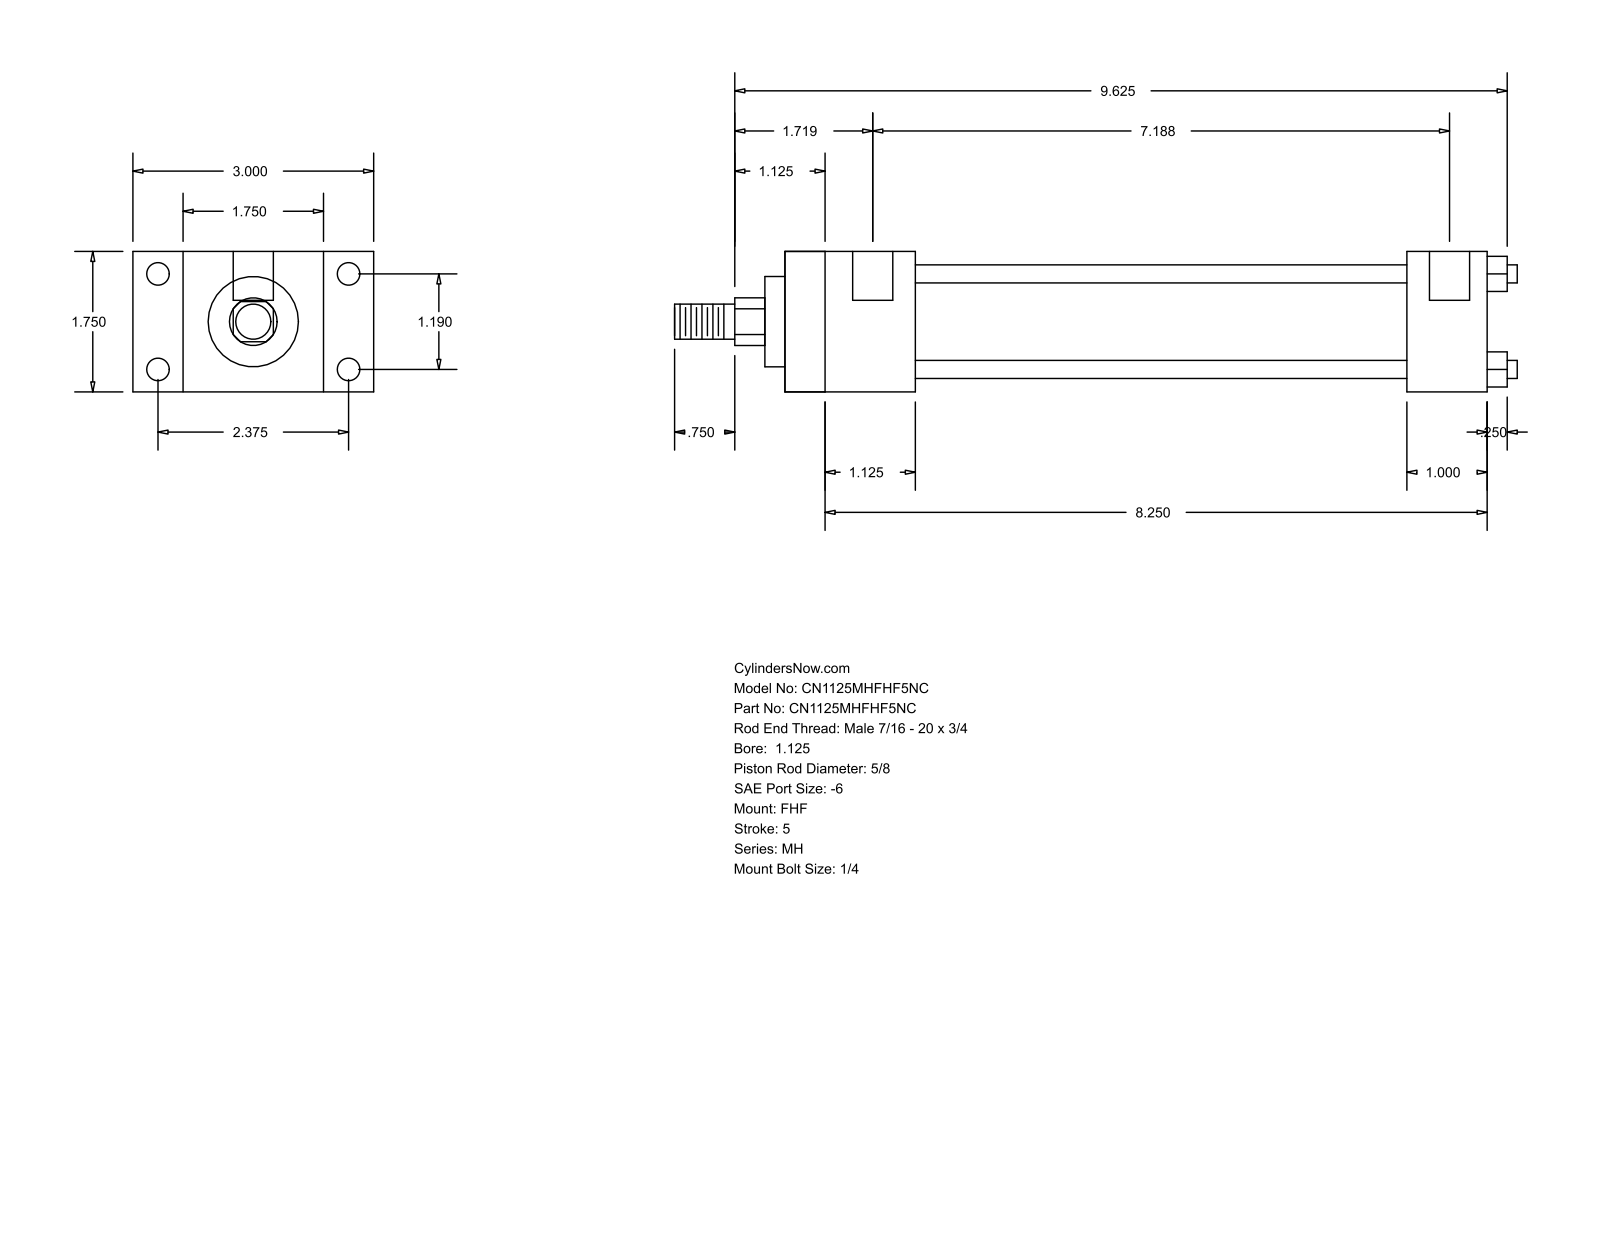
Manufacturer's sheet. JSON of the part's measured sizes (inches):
{"part_name": "MH_FHF__0112_0.625", "step_written_by": "GSSL Pune (CONFIG_CONTROL_DESIGN)", "units": "inches", "bodies": {"solids": 0, "faces": 88, "planar": 60, "cylindrical": 28, "other": 0}, "overall_size": [10.5, 3, 1.75], "round_holes": [[0.219, 4], [0.281, 4], [0.5, 2]], "round_bosses_or_shafts": [[0.225, 4], [1.375, 1], [1.125, 1], [0.625, 1], [0.437, 1]], "partial_cylinders_radius": [[0.297, 1]], "face_to_face_distances": [1.75, 0.625, 2.375, 1.625, 3, 8.75, 7.125, 1, 7.75, 6.125], "hole_center_spacings": [1.19, 2.375, 2.656, 7.063, 0.125, 7.187]}
